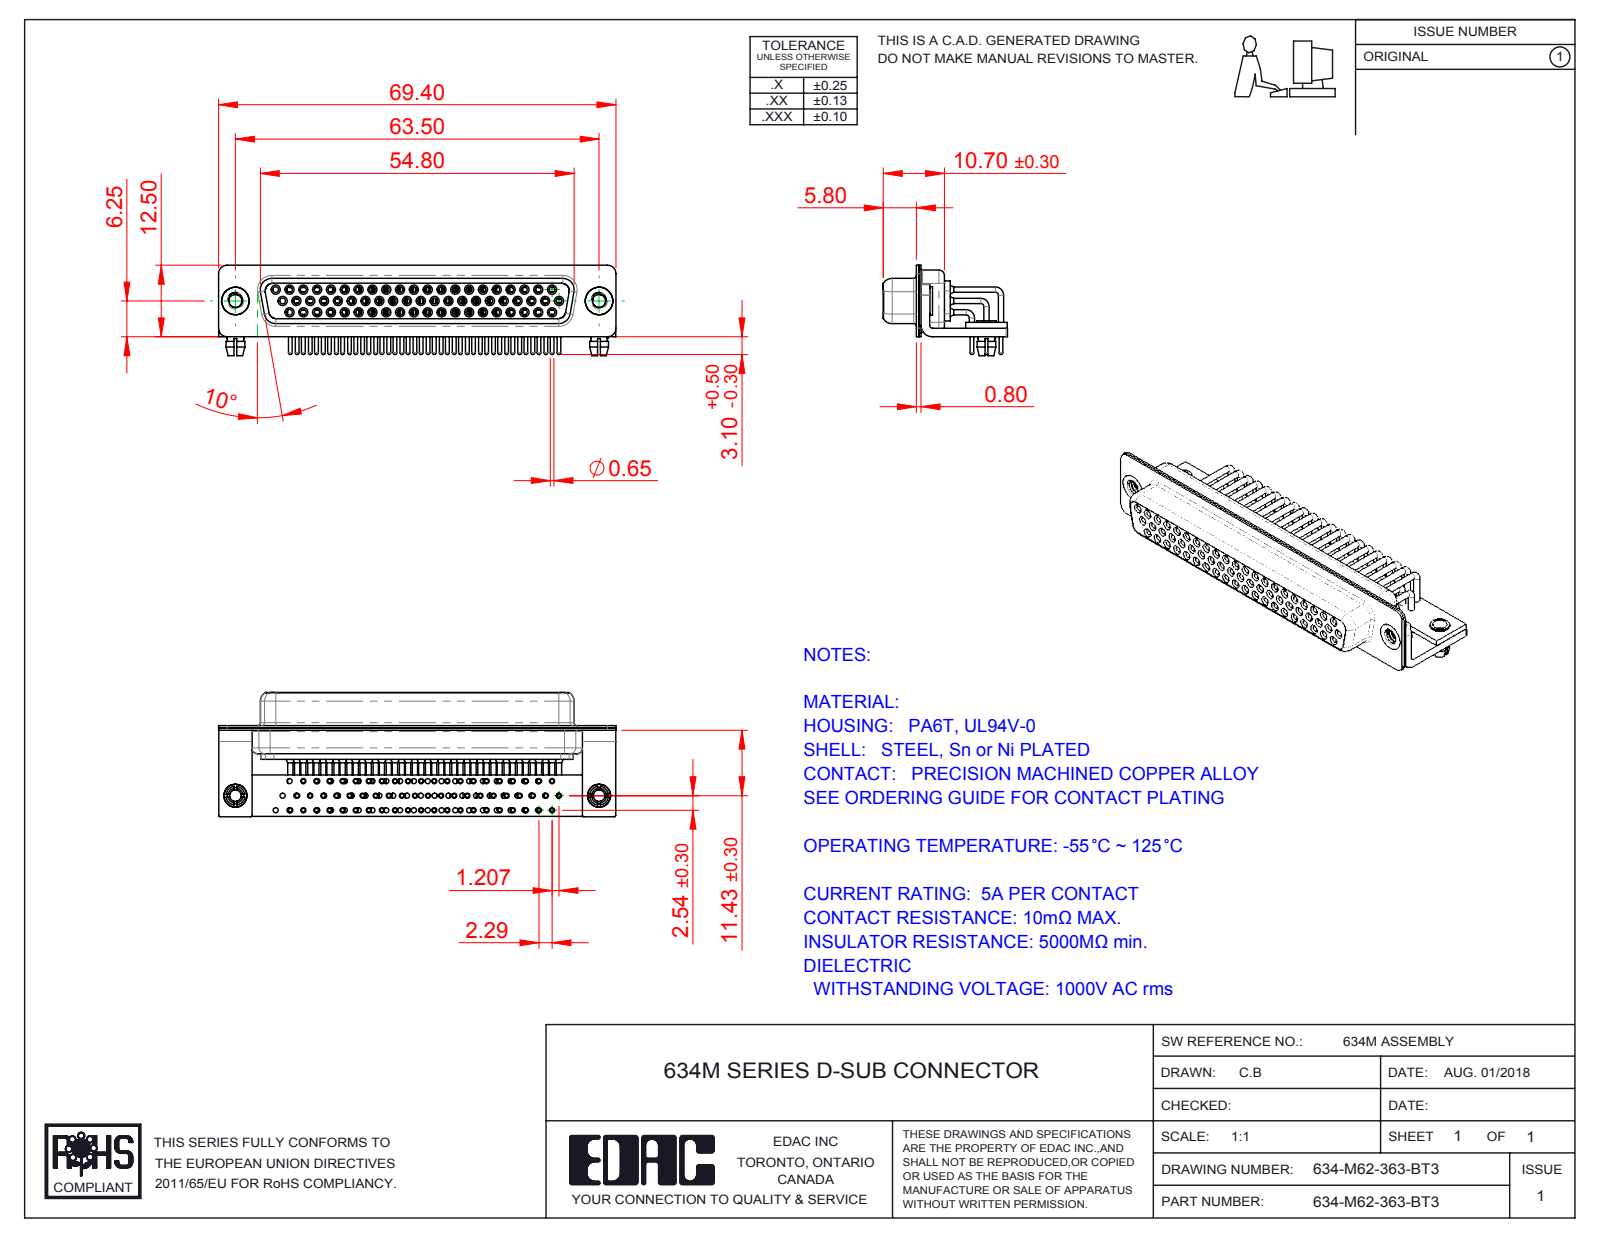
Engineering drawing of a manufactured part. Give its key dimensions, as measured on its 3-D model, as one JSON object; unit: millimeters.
{"part_name": "634M Shell Front_62 Contacts; 634M Stabilizer Board_62 Contacts; 634M Contact Row 2; 634M 4-40 Threaded Rivet_Stabilizer (+7 more)", "step_written_by": "SolidWorks 2016 (CONFIG_CONTROL_DESIGN)", "units": "millimeters", "bodies": {"solids": 72, "faces": 3831, "planar": 1071, "cylindrical": 1741, "other": 1019}, "overall_size": [69.4, 21.7, 15.8], "volume_mm3": 6178, "surface_area_mm2": 19963, "round_holes": [[2, 64], [0.9, 62], [1, 62], [1.1, 62], [1.7, 62], [1.8, 62], [2.26, 2], [2.5, 2], [3.2, 2], [4, 2], [4.8, 2]], "round_bosses_or_shafts": [[0.9, 118], [1.6, 62], [1.5, 62], [0.65, 62], [2, 56], [5, 2], [4.9, 2], [4, 2]], "partial_cylinders_radius": [[0.25, 16], [1.5, 16], [2, 13], [1.35, 8], [1.6, 8], [0.5, 5], [0.6, 4], [0.65, 4]], "face_to_face_distances": [0.4, 2.3, 1, 1.9, 1.45, 8.95, 8.5, 0.85, 0.8, 9.35], "hole_center_spacings": [7.24, 2.41, 9.65, 4.83, 14.48, 16.89, 2.81, 2.32]}
